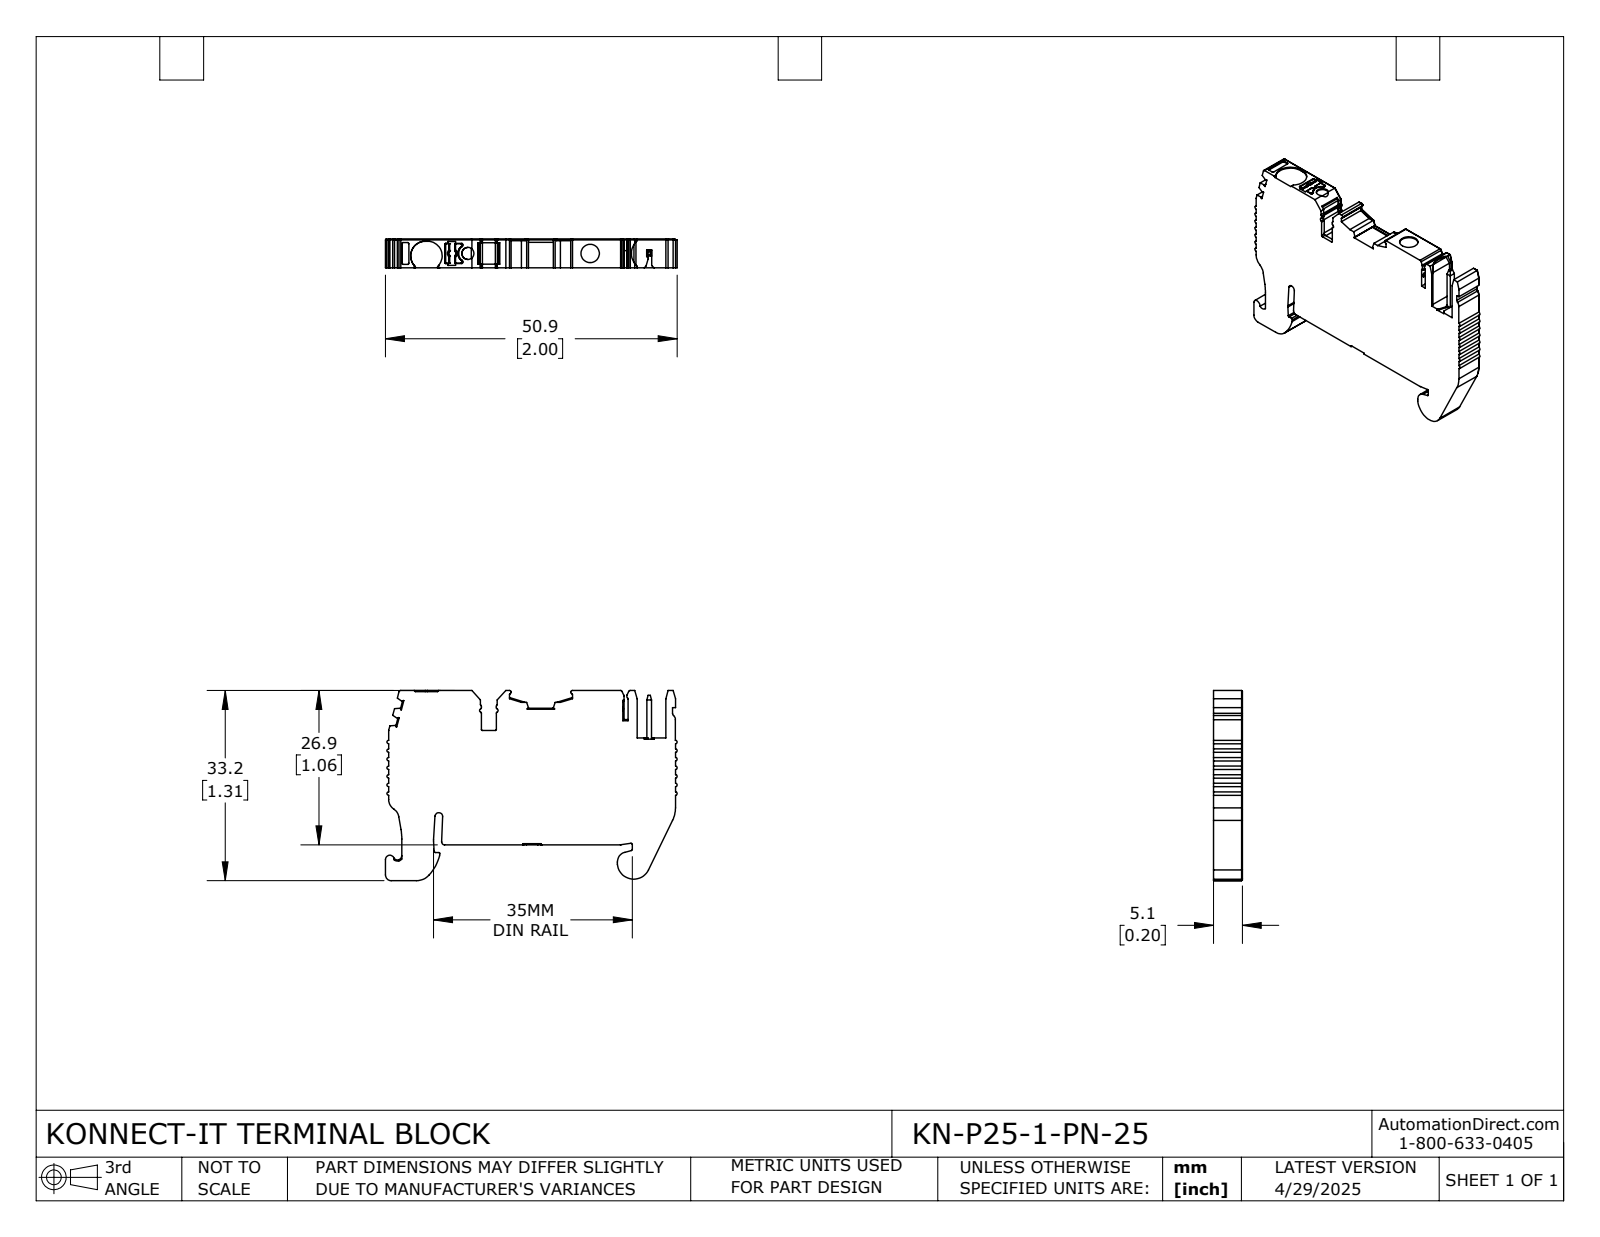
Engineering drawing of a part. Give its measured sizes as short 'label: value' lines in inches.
name: KN-P25-1-PN-25
written by: SolidWorks 2024 (CONFIG_CONTROL_DESIGN)
unit: in
bodies: 1 solid, 461 faces (263 planar, 179 cylindrical, 19 other)
size: 2.005 × 1.307 × 0.199
volume: 0.397 in³; area: 6.012 in²
holes: 1× ⌀0.083, 1× ⌀0.126
rounds: 35× R0.012, 34× R0.008, 13× R0.02, 9× R0.004, 8× R0.016, 4× R0.006, 3× R0.024, 3× R0.035
face distances: 0.199, 1.061, 1.053, 1.971, 1.905, 0.067, 0.981, 0.205, 1.7, 0.271
hole spacings: 0.841
